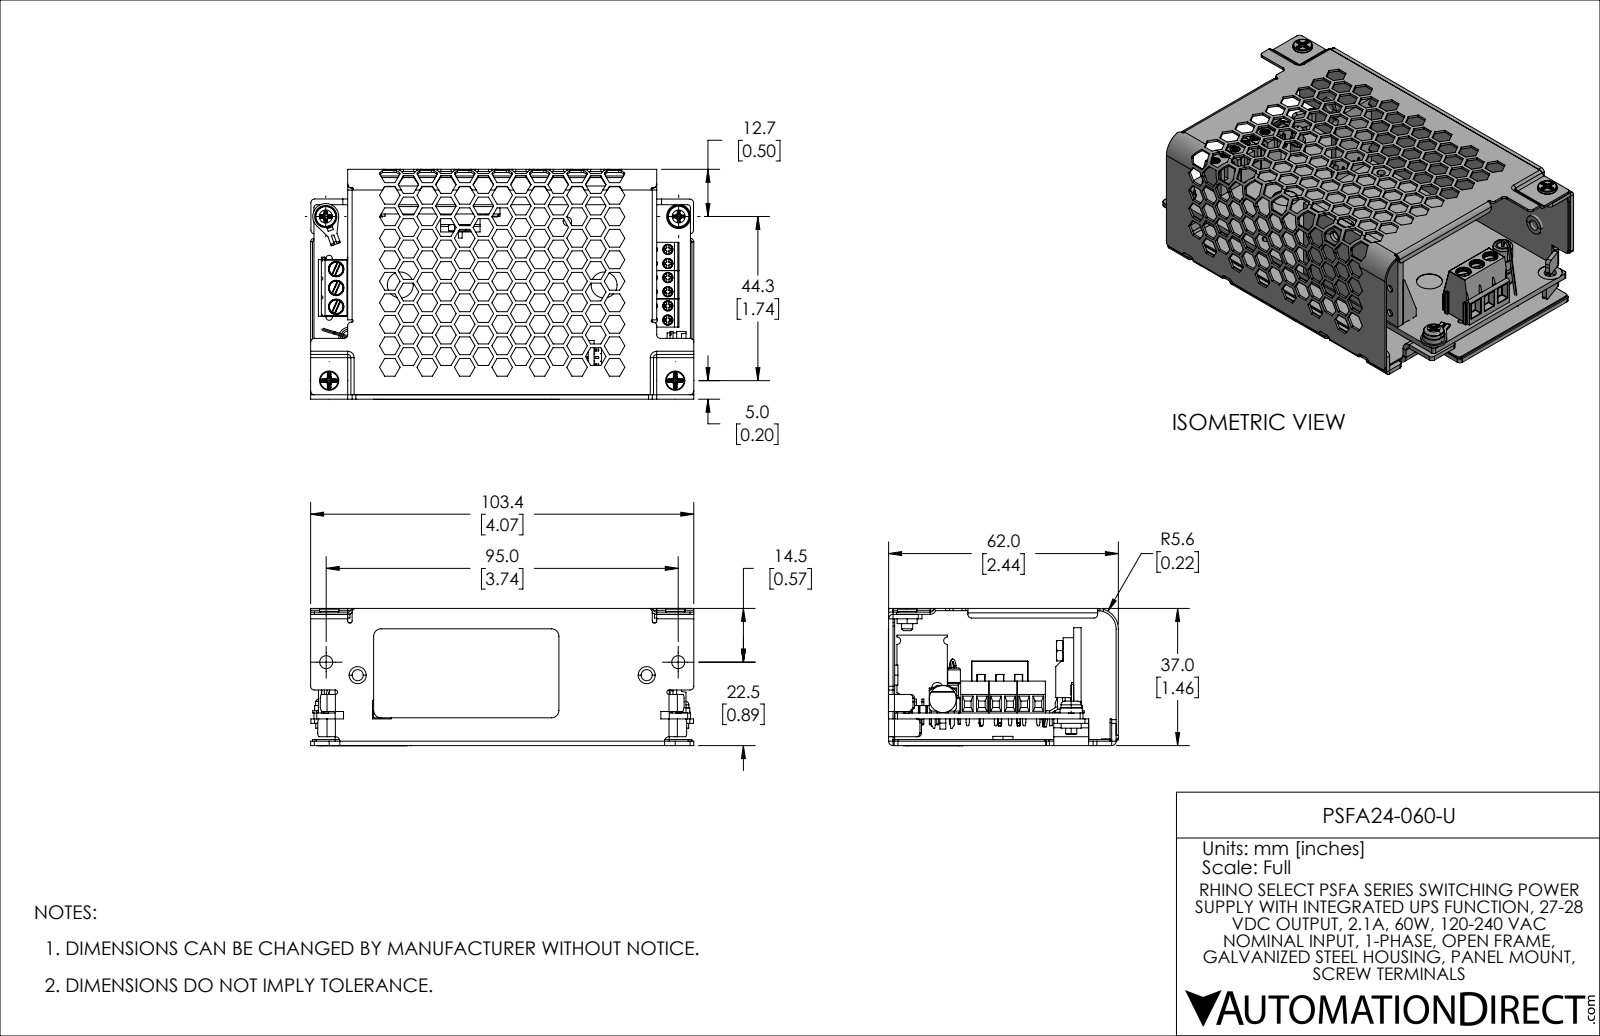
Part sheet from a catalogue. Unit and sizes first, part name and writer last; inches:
Units: inches
Overall size (bounding box): 4.071 × 2.443 × 1.459
Round holes (diameter × count): ⌀0.118 ×9, ⌀0.051 ×6, ⌀0.065 ×6, ⌀0.108 ×6, ⌀0.157 ×5, ⌀0.079 ×4, ⌀0.13 ×4, ⌀0.256 ×4, ⌀0.059 ×3, ⌀0.067 ×3, ⌀0.158 ×3, ⌀0.091 ×2
Round bosses / shafts (diameter × count): ⌀0.213 ×8, ⌀0.106 ×6, ⌀0.102 ×4, ⌀0.154 ×3, ⌀0.236 ×2, ⌀0.217 ×2, ⌀0.205 ×2, ⌀0.026 ×2
Partial cylindrical surfaces — rounded edges, fillets, slot ends (radius × count): R0.004 ×178, R0.039 ×85, R0.005 ×64, R0.047 ×13, R0.024 ×9, R0.013 ×6, R0.02 ×6, R0.033 ×6
Main face-to-face distances: 0.047, 0.017, 0.064, 0.063, 0.299, 0.346, 0.282, 0.236, 0.283, 0.219
Hole centre spacings: 0.15, 0.156, 2.824, 0.3, 0.312, 2.165, 2.922, 0.106
Volume: 2.085 in³ · Surface area: 115.2 in²
Bodies: 28 solids, 4021 faces (2767 planar, 741 cylindrical, 513 other)
Part name (STEP PRODUCT): PSFA24-060-U_1
STEP written by: SolidWorks 2021 (AUTOMOTIVE_DESIGN)
